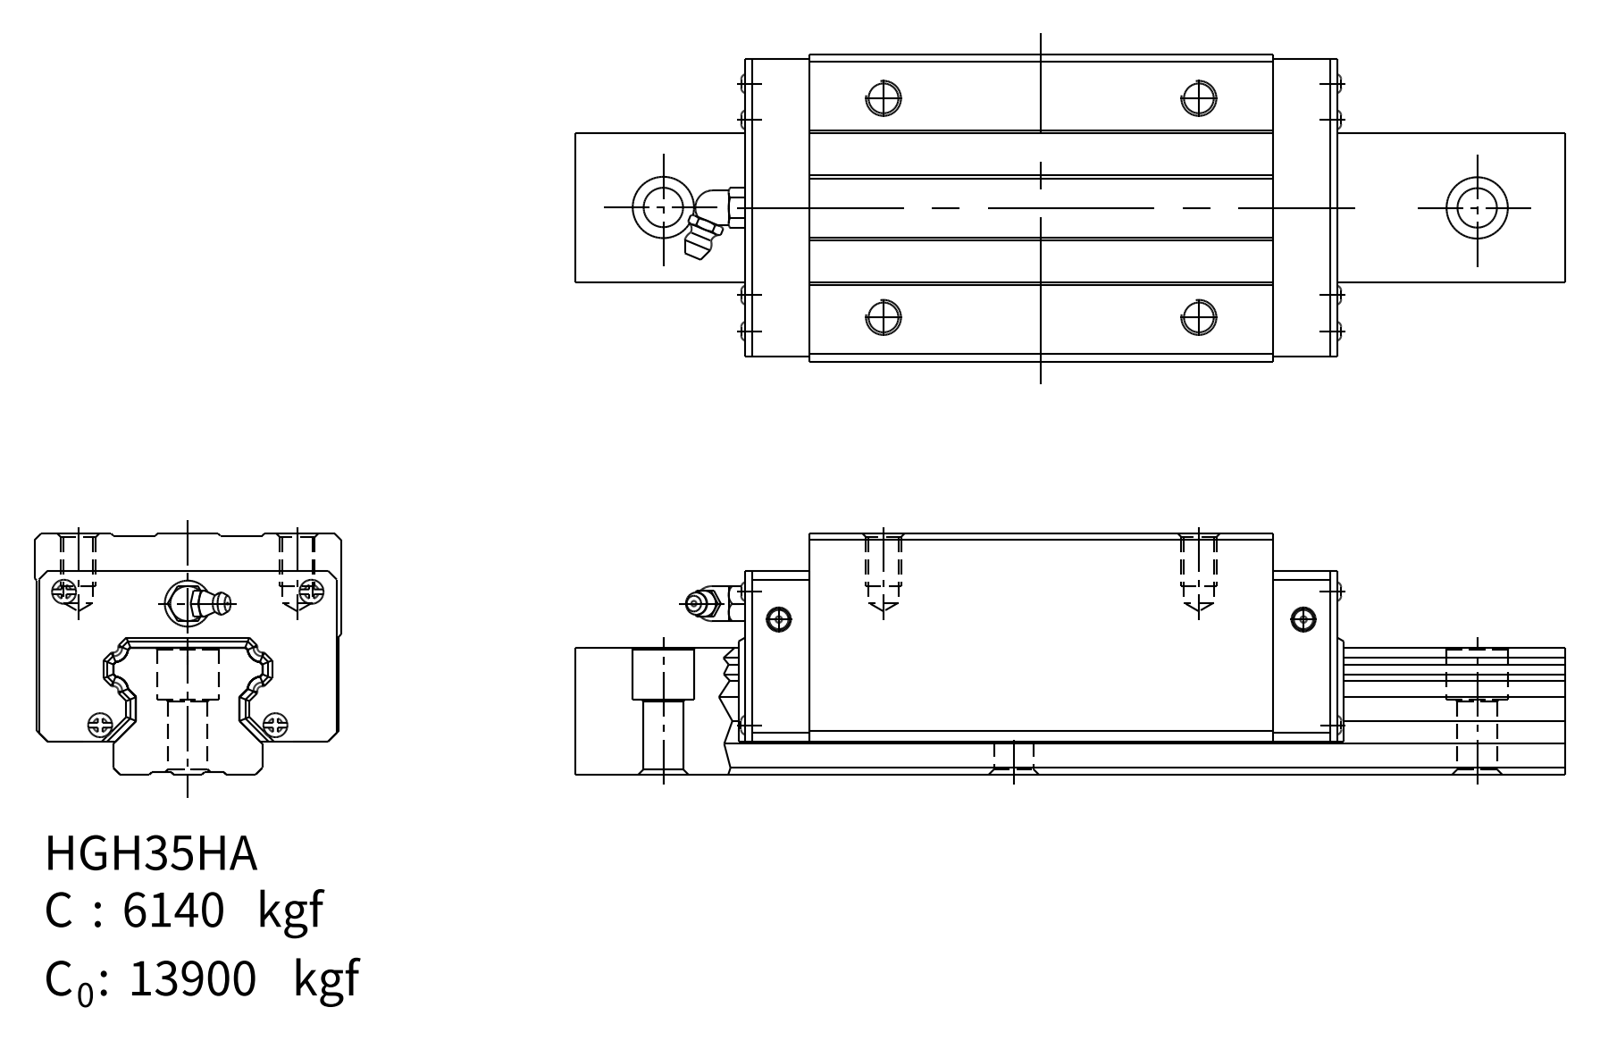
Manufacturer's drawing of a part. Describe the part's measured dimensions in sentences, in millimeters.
The part is named "HGH35HA". Its 3-D file was written by "SolidWorks 2006104 (CONFIG_CONTROL_DESIGN)". It is 1 solid with 373 faces: 297 planar, 16 cylindrical and 60 other. Overall it measures 138.5 by 70 by 47.5 millimeters. Its volume is 347 317 cubic millimeters and its surface area 44 569 square millimeters. Round holes: 4 of diameter 8. Partial cylindrical surfaces (rounded edges, fillets, slot ends): 4 of radius 1.2, 4 of radius 3.25. The main face-to-face distances are 0.5, 47.5, 21.5, 26, 69.5, 69, 47, 25.5, 138.2, 39.05. The hole center spacings are 50, 72, 87.66.
